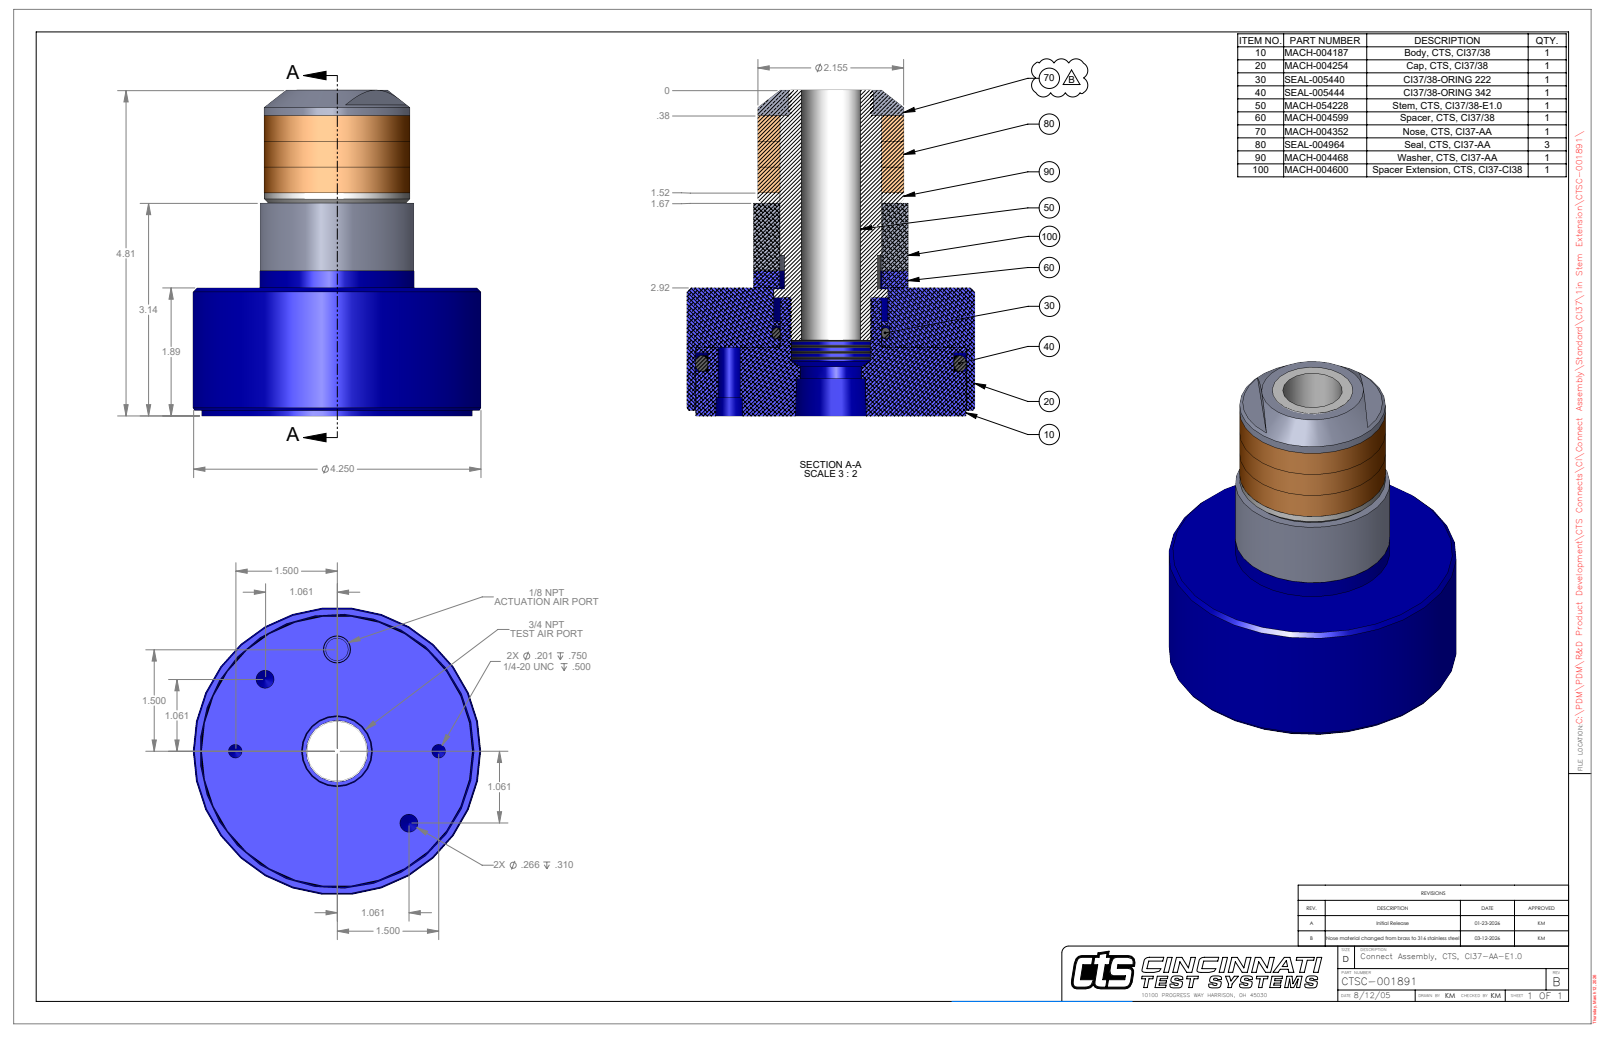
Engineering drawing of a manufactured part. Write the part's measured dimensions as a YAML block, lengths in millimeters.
part_name: "CTSC-001891"
step_written_by: "SolidWorks 2023 (AUTOMOTIVE_DESIGN)"
units: millimeters
bodies: {solids: 8, faces: 78, planar: 37, cylindrical: 28, other: 13}
overall_size: [122.25, 107.95, 107.95]
volume: 561249
surface_area: 92938
round_holes:
  - {diameter: 5.11, count: 2}
  - {diameter: 6.75, count: 2}
  - {diameter: 22.35, count: 1}
  - {diameter: 23.01, count: 1}
  - {diameter: 29.77, count: 1}
  - {diameter: 37.97, count: 1}
  - {diameter: 38.35, count: 1}
  - {diameter: 42.88, count: 1}
  - {diameter: 101.6, count: 1}
round_bosses_or_shafts:
  - {diameter: 107.95, count: 1}
  - {diameter: 101.4, count: 1}
  - {diameter: 57.94, count: 1}
  - {diameter: 54.74, count: 1}
  - {diameter: 42.52, count: 1}
  - {diameter: 38.05, count: 1}
  - {diameter: 31.75, count: 1}
face_to_face_distances: [48.08, 9.65, 19.31, 54.43, 6.35, 112.65, 64.57, 58.22, 31.75, 93.34]
hole_center_spacings: [38.1, 29.16, 70.4, 76.2]
